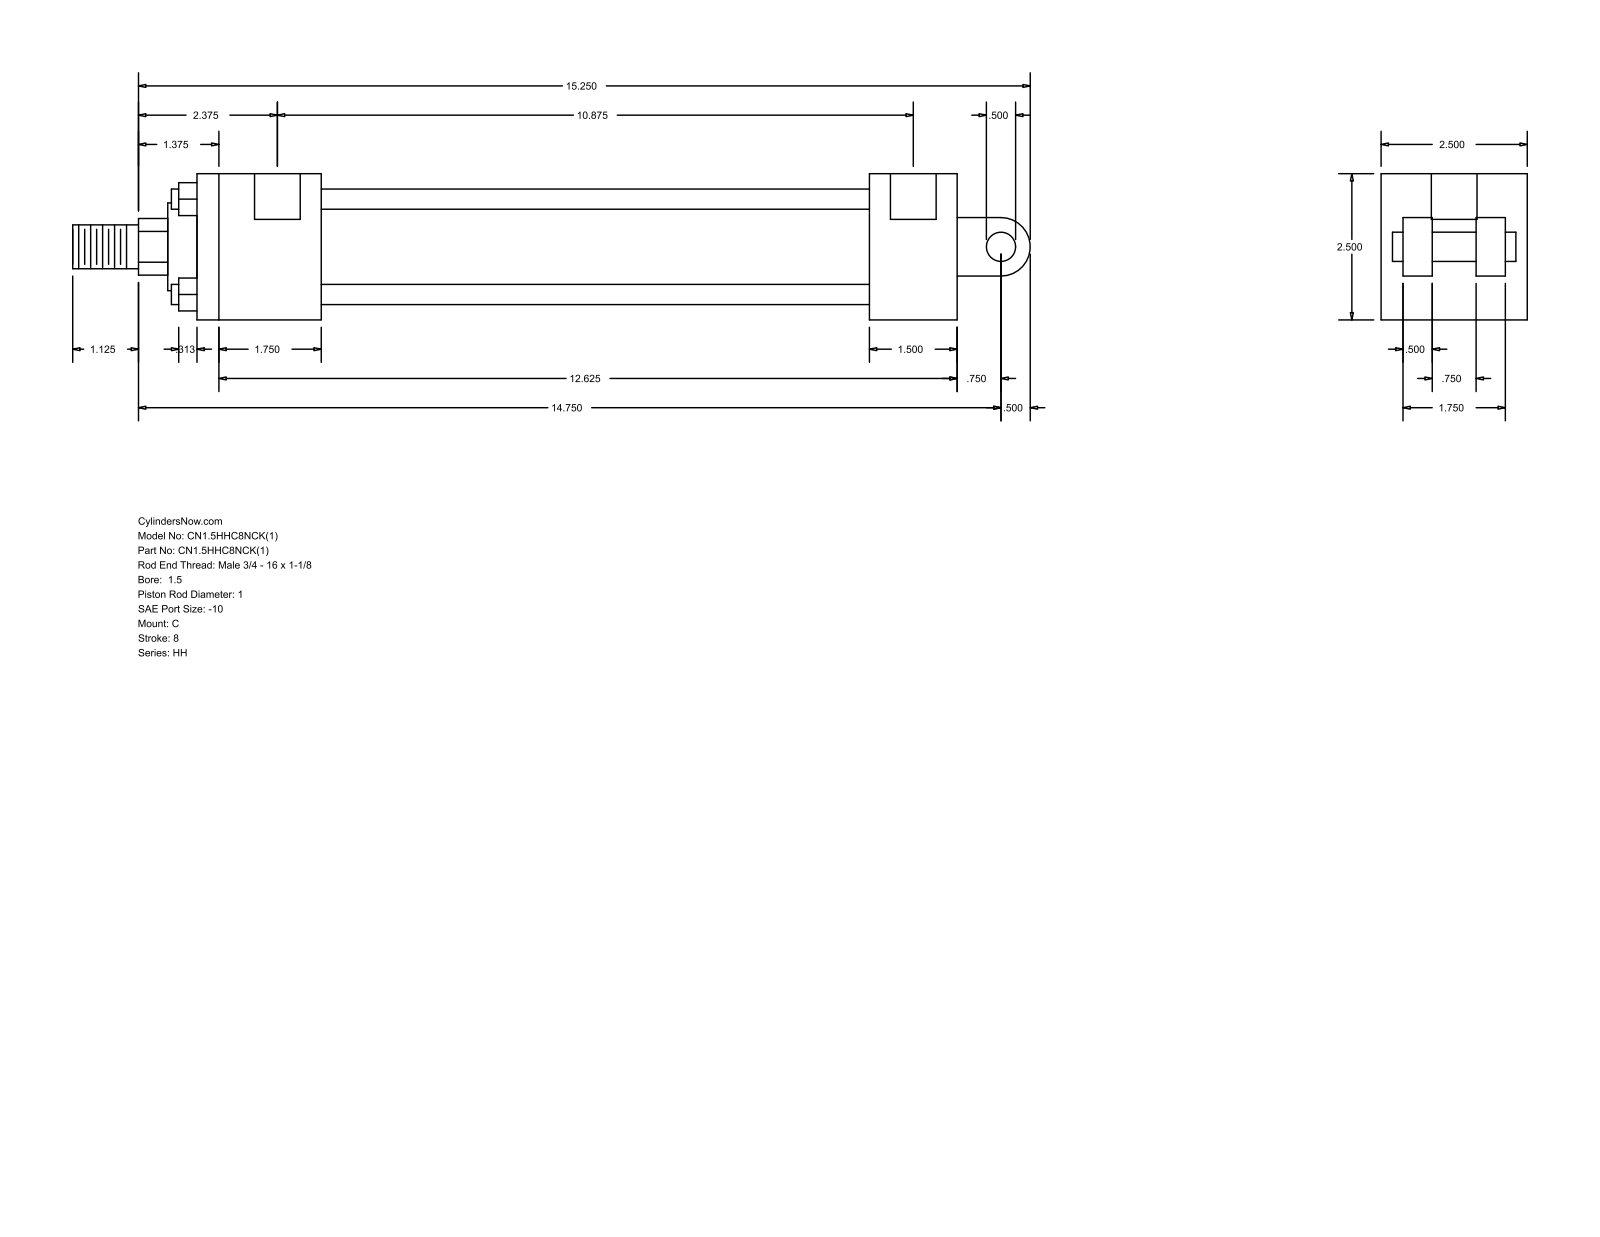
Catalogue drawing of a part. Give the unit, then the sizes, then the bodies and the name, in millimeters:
Units: millimetres
Overall size (bounding box): 415.93 × 63.5 × 63.5
Round holes (diameter × count): ⌀5.56 ×4, ⌀19.84 ×2
Round bosses / shafts (diameter × count): ⌀8.76 ×4, ⌀44.45 ×1, ⌀38.1 ×1, ⌀25.4 ×1, ⌀19.05 ×1, ⌀12.7 ×1
Partial cylindrical surfaces — rounded edges, fillets, slot ends (radius × count): R12.29 ×1, R12.7 ×1
Main face-to-face distances: 63.5, 53.98, 38.1, 238.12, 276.22, 292.1, 330.2, 12.7, 9.52, 22.22
Hole centre spacings: 1.59, 277.81, 279.4, 276.22
Bodies: 0 solids, 99 faces (70 planar, 29 cylindrical, 0 other)
Part name (STEP PRODUCT): HH_C__0150_1
STEP written by: GSSL Pune (CONFIG_CONTROL_DESIGN)
